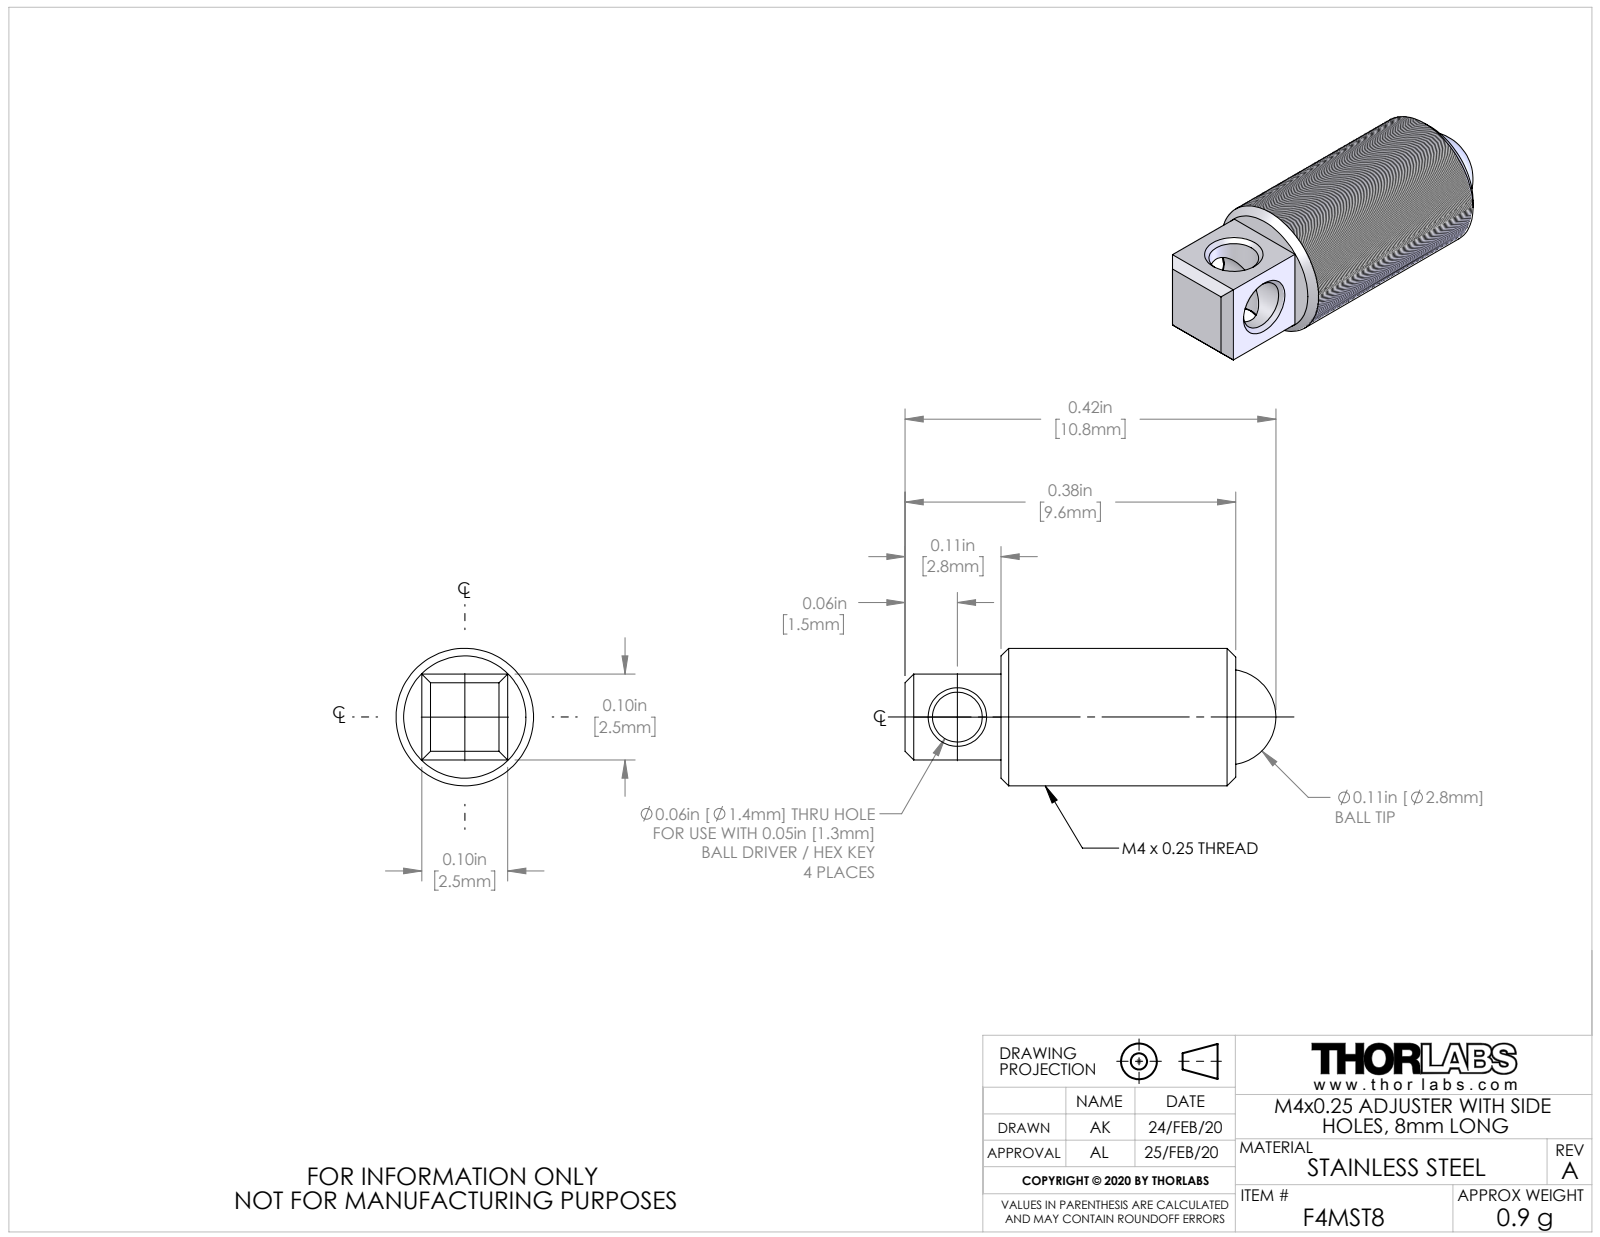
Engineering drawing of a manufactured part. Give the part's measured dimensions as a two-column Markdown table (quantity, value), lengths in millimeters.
| quantity | value |
| --- | --- |
| part name | TTN203594-E0W |
| STEP written by | SolidWorks 2018 (AUTOMOTIVE_DESIGN) |
| units | millimeters |
| bodies | 2 solids, 41 faces (11 planar, 12 cylindrical, 18 other) |
| overall size | 10.8 × 4 × 4 |
| volume | 100 mm³ |
| surface area | 174 mm² |
| round holes (diameter × count) | 1.4 × 2, 2.8 × 1 |
| round bosses / shafts (diameter × count) | 4 × 1 |
| main face-to-face distances | 2.5, 2.8, 6.8, 9.6 |
